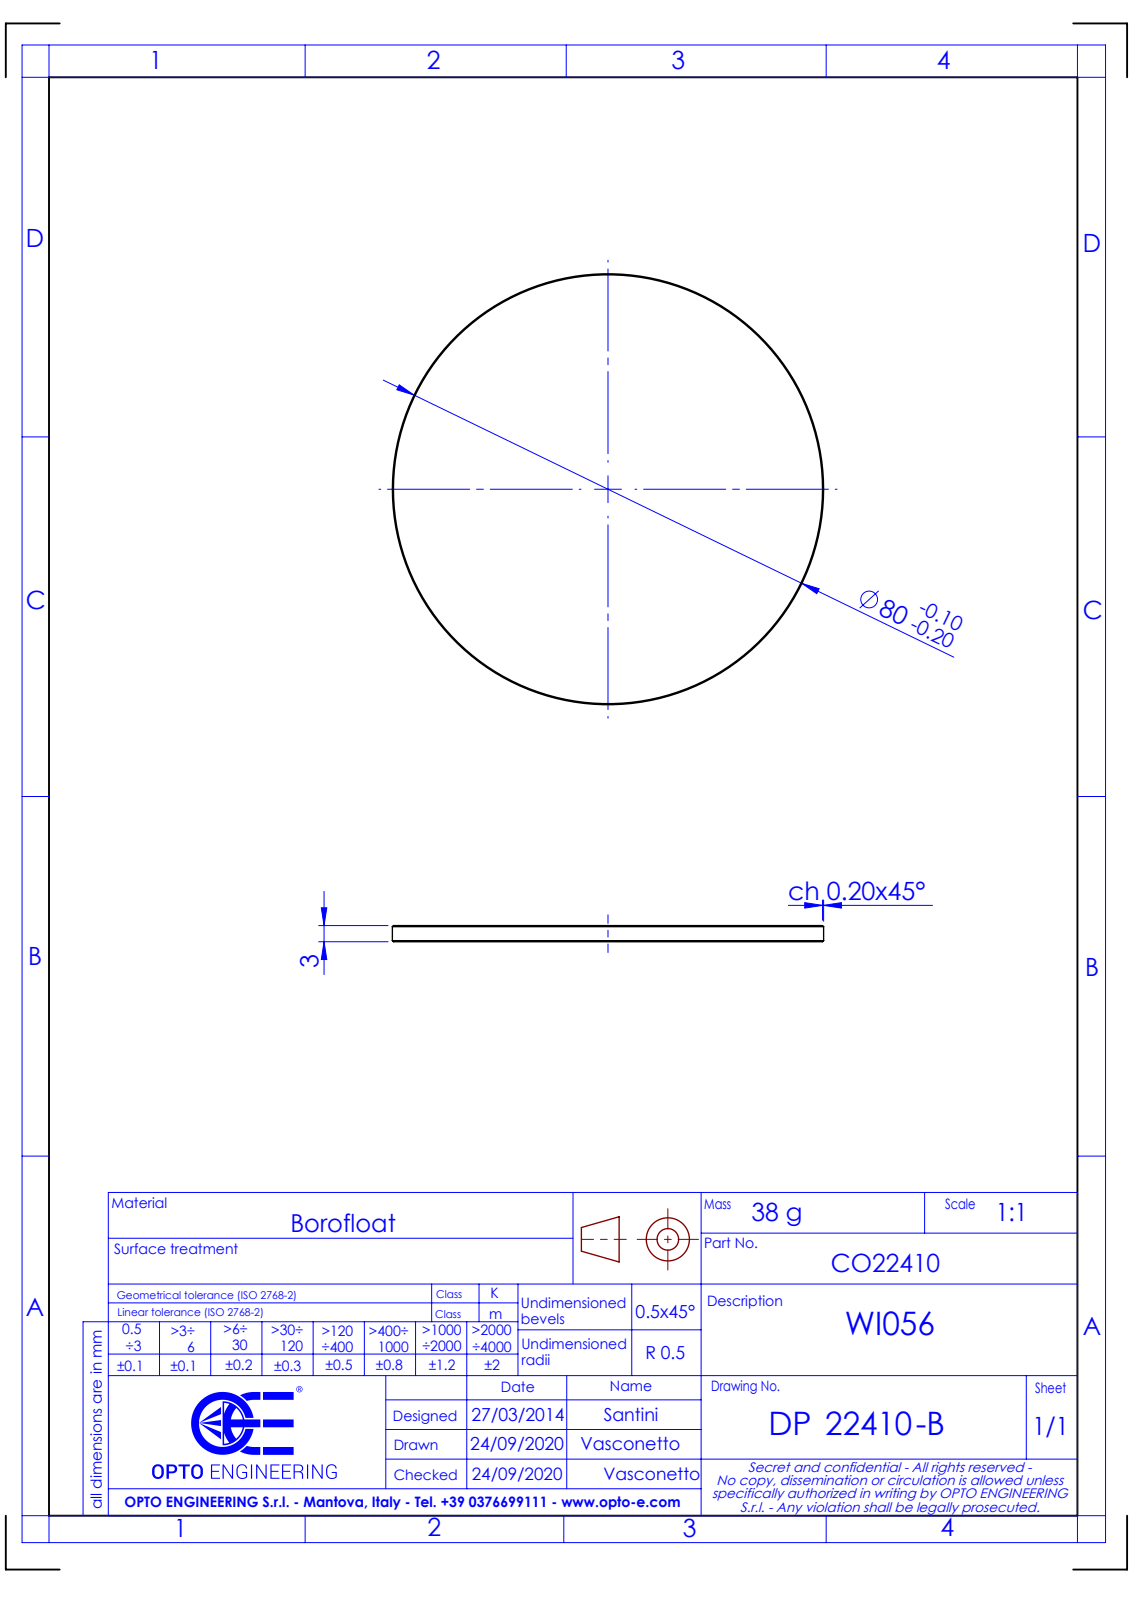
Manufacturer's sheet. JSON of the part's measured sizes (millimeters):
{"part_name": "DP22410_WI056", "step_written_by": "SolidWorks 2021 (CONFIG_CONTROL_DESIGN)", "units": "millimeters", "bodies": {"solids": 1, "faces": 8, "planar": 2, "cylindrical": 2, "other": 4}, "overall_size": [80, 80, 3], "volume_mm3": 15070, "surface_area_mm2": 10748, "round_bosses_or_shafts": [[80, 1]], "face_to_face_distances": [3]}
